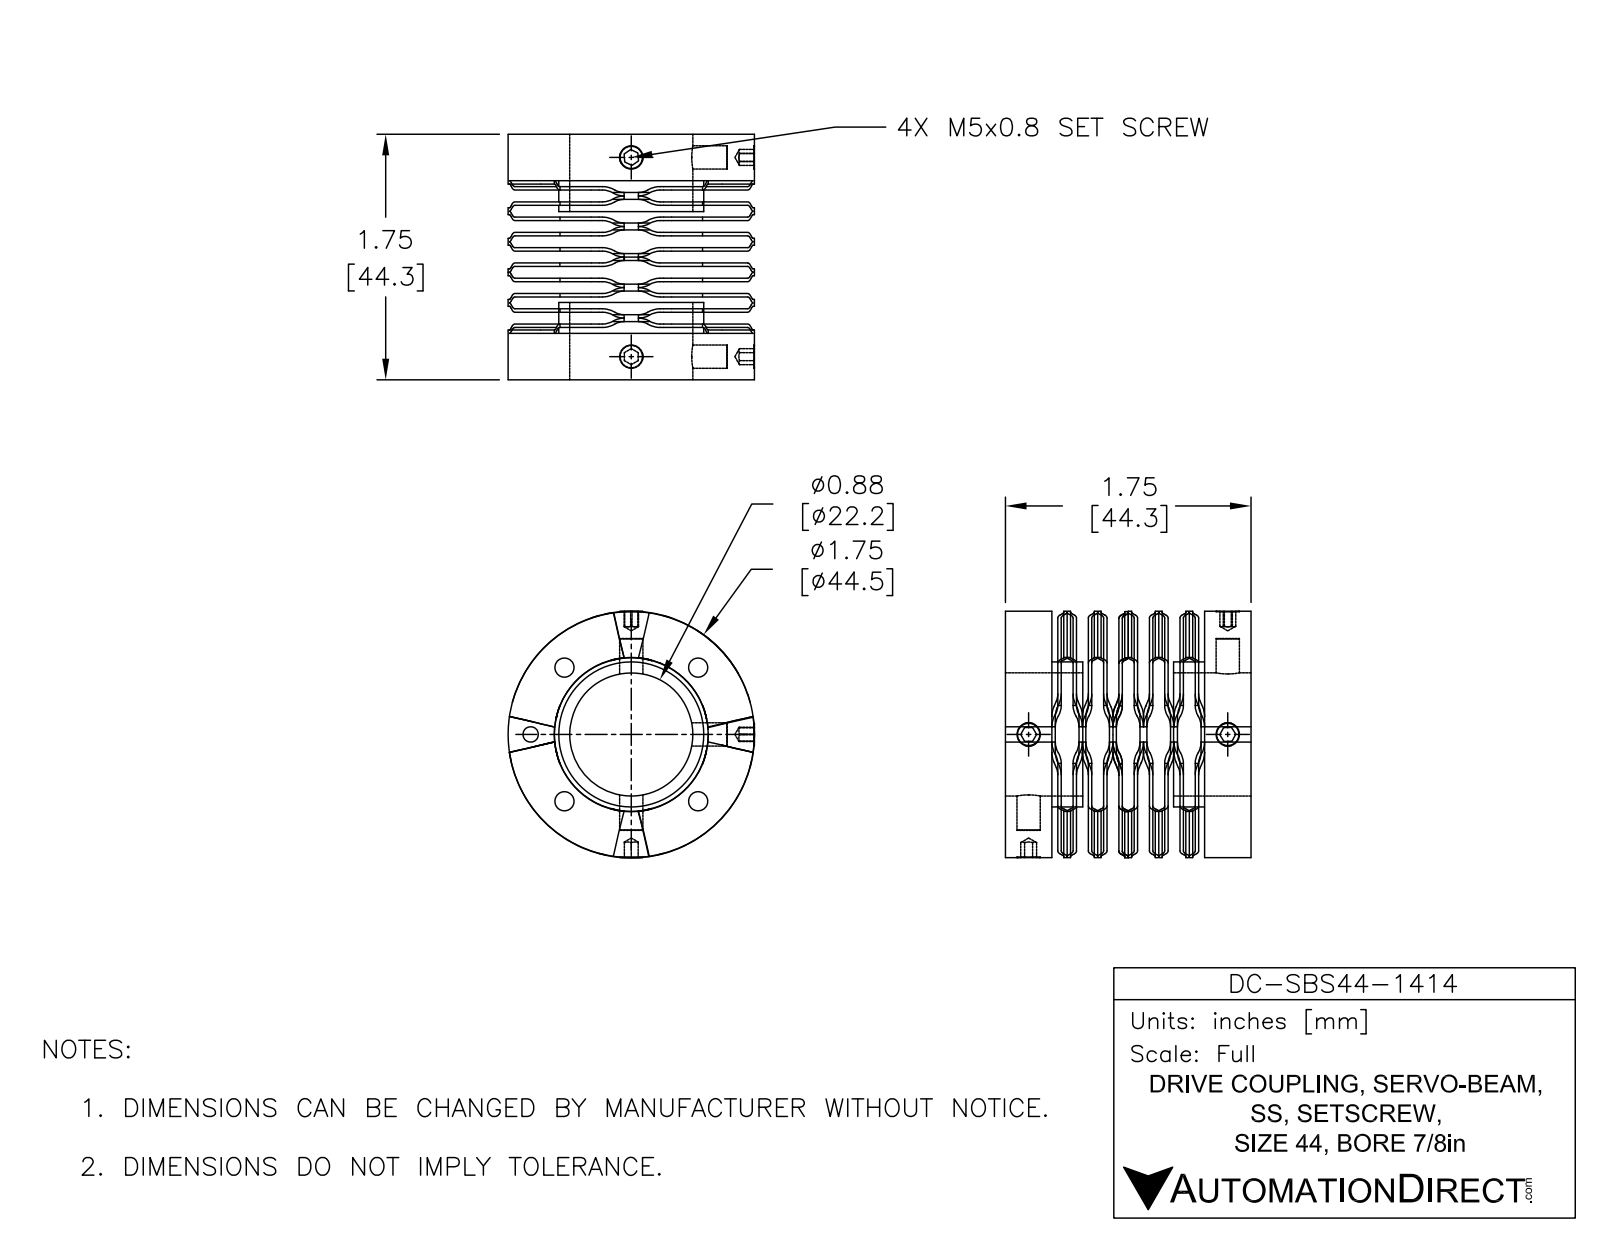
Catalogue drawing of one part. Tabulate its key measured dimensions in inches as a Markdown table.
| quantity | value |
| --- | --- |
| part name | DC-SBS44-1414 |
| STEP written by | SolidWorks 2015 (AUTOMOTIVE_DESIGN) |
| units | inches |
| bodies | 16 solids, 798 faces (362 planar, 428 cylindrical, 8 other) |
| overall size | 1.752 × 1.751 × 1.743 |
| volume | 1.655 in³ |
| surface area | 49.98 in² |
| round holes (diameter × count) | 0.136 × 4, 0.165 × 4, 0.109 × 1, 0.875 × 1, 1.094 × 1 |
| round bosses / shafts (diameter × count) | 0.165 × 3, 1.75 × 1, 0.165 × 1 |
| partial cylindrical surfaces (radius × count) | 0.071 × 320 |
| main face-to-face distances | 0.217, 0.433, 0.65, 0.108, 0.024, 0.083, 0.109, 0.192, 0.3, 0.133 |
| hole center spacings | 0.672, 0.95, 1.343, 0.53, 0.531, 0.711, 0.95, 1.277 |
